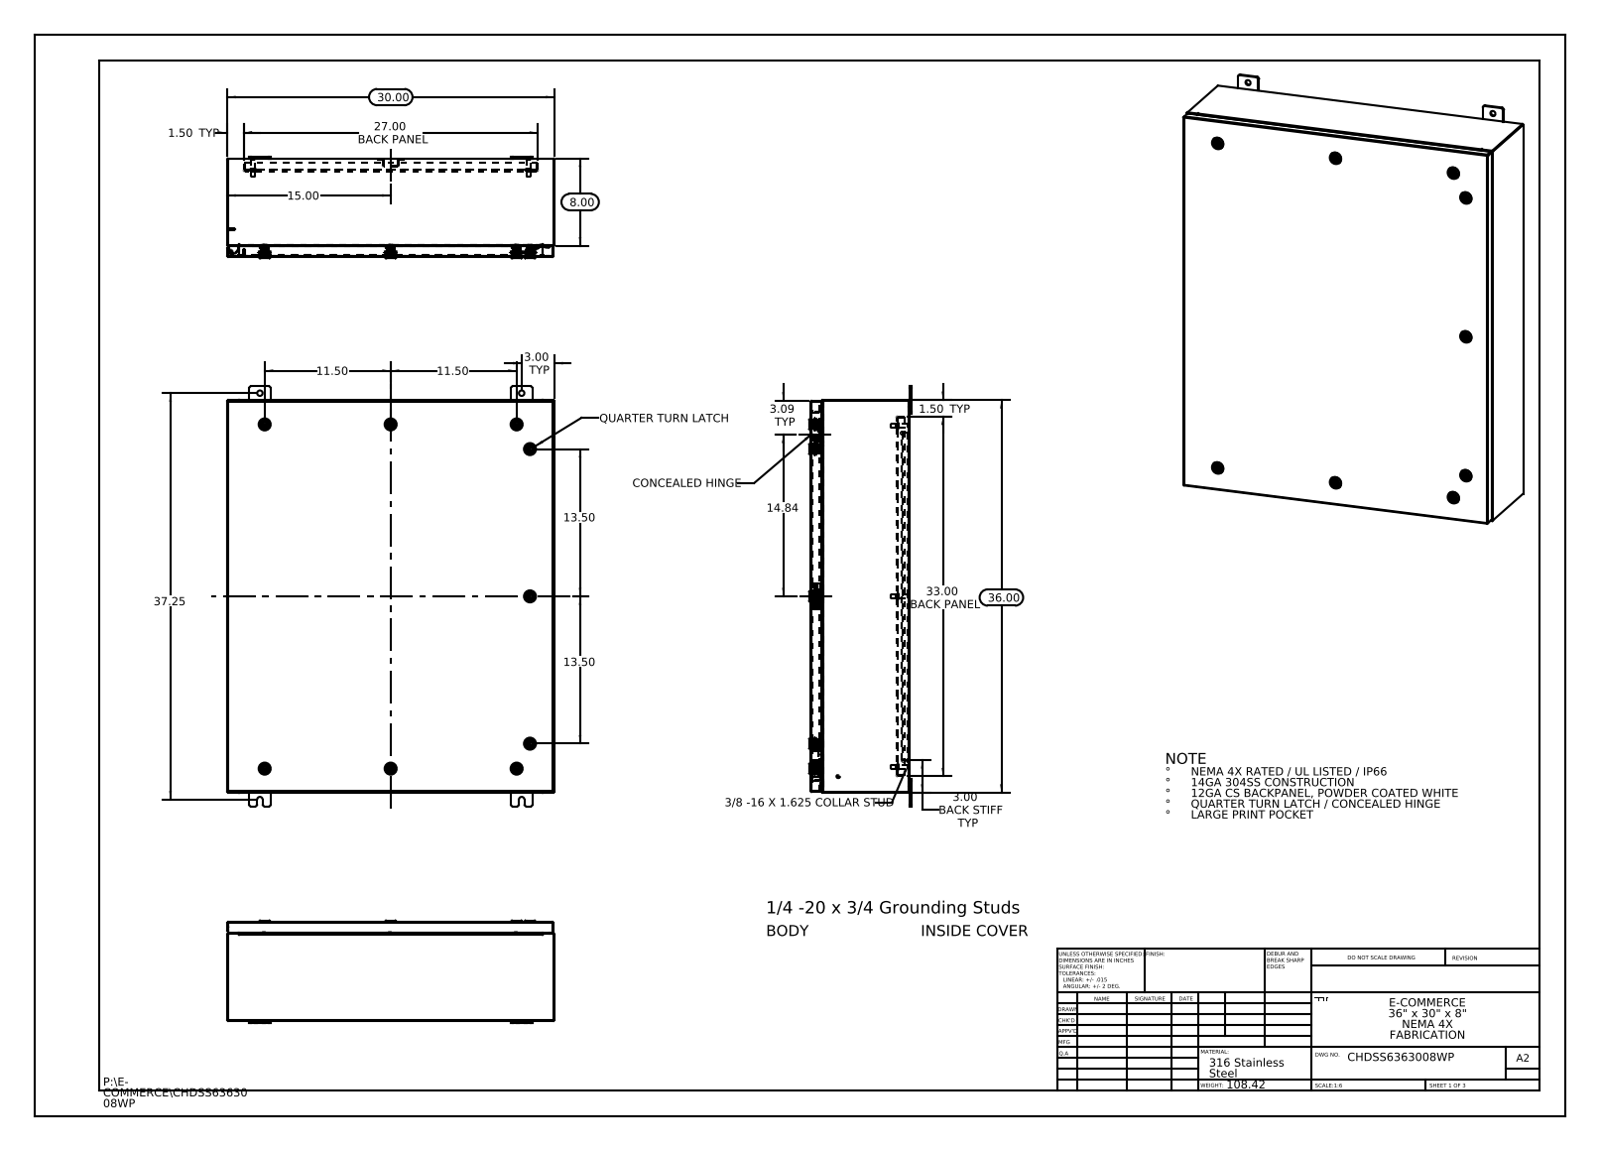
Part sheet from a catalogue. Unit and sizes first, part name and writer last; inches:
Units: inches
Overall size (bounding box): 38.5 × 30 × 9.356
Round holes (diameter × count): ⌀0.5 ×10, ⌀0.197 ×9, ⌀0.394 ×9, ⌀0.4 ×9, ⌀0.63 ×9, ⌀0.787 ×9, ⌀0.136 ×6, ⌀0.211 ×1
Round bosses / shafts (diameter × count): ⌀0.236 ×11, ⌀1.102 ×9, ⌀0.78 ×9, ⌀0.626 ×9, ⌀0.61 ×9, ⌀0.531 ×9, ⌀0.392 ×9, ⌀0.114 ×9
Partial cylindrical surfaces — rounded edges, fillets, slot ends (radius × count): R0.006 ×297, R0.118 ×297, R0.028 ×108, R0.02 ×36, R0.197 ×36, R0.013 ×26, R0.19 ×24, R0.088 ×22
Main face-to-face distances: 0.075, 0.074, 9.01, 8.935, 8.936, 8.861, 0.104, 1, 1.075, 7.861
Hole centre spacings: 11.55, 15.625, 29.694, 33.598, 25.25, 31.55, 0.688, 1.858
Volume: 385.3 in³ · Surface area: 9 528 in²
Bodies: 78 solids, 8020 faces (2324 planar, 2502 cylindrical, 3194 other)
Part name (STEP PRODUCT): CHDSS6363008WP Top; Quarter-20 CD Stud; CHDSS6363008WP Cover; CHDSS6363008WP Bottom (+8 more)
STEP written by: SolidWorks 2013 (CONFIG_CONTROL_DESIGN)
